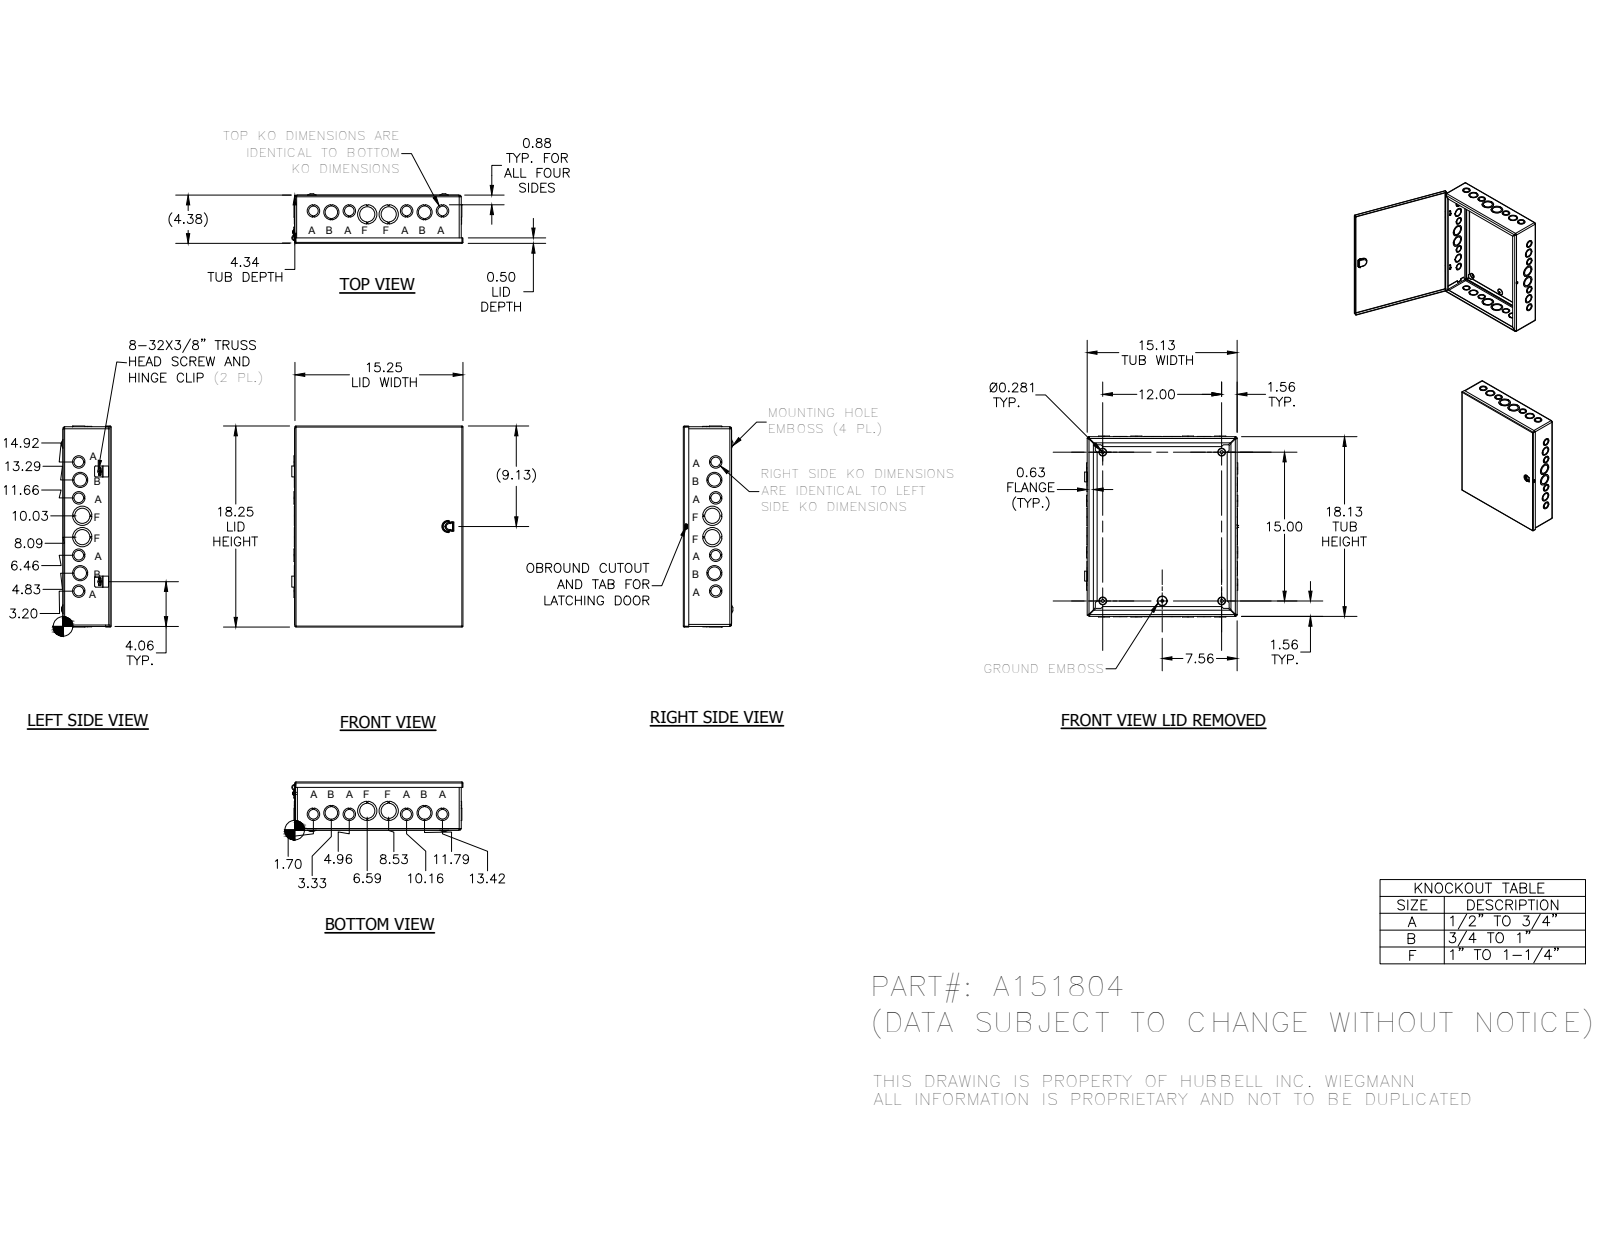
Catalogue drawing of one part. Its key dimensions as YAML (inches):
part_name: "A1518BA; A151804WRA; 31816; 372177 (+3 more)"
step_written_by: "Autodesk Inventor 2014 (AUTOMOTIVE_DESIGN)"
units: inches
bodies: {solids: 39, faces: 1391, planar: 934, cylindrical: 299, other: 158}
overall_size: [18.437, 15.637, 4.504]
round_holes:
  - {diameter: 1.125, count: 12}
  - {diameter: 0.875, count: 8}
  - {diameter: 1.375, count: 8}
  - {diameter: 0.3, count: 4}
  - {diameter: 1.75, count: 4}
  - {diameter: 0.14, count: 2}
  - {diameter: 0.165, count: 1}
round_bosses_or_shafts:
  - {diameter: 0.384, count: 2}
  - {diameter: 0.164, count: 2}
  - {diameter: 0.228, count: 1}
partial_cylinders:
  - {radius: 0.125, count: 15}
  - {radius: 0.031, count: 10}
  - {radius: 0.063, count: 8}
  - {radius: 0.094, count: 8}
  - {radius: 0.187, count: 8}
  - {radius: 0.055, count: 4}
  - {radius: 0.062, count: 4}
  - {radius: 0.07, count: 4}
face_to_face_distances: [0.062, 4.316, 4.254, 0.062, 0.063, 4.317, 4.379, 18.063, 15.125, 15.063]
hole_center_spacings: [1.635, 1.659, 3.265, 3.584, 5.204, 6.831, 8.46, 1.635]
